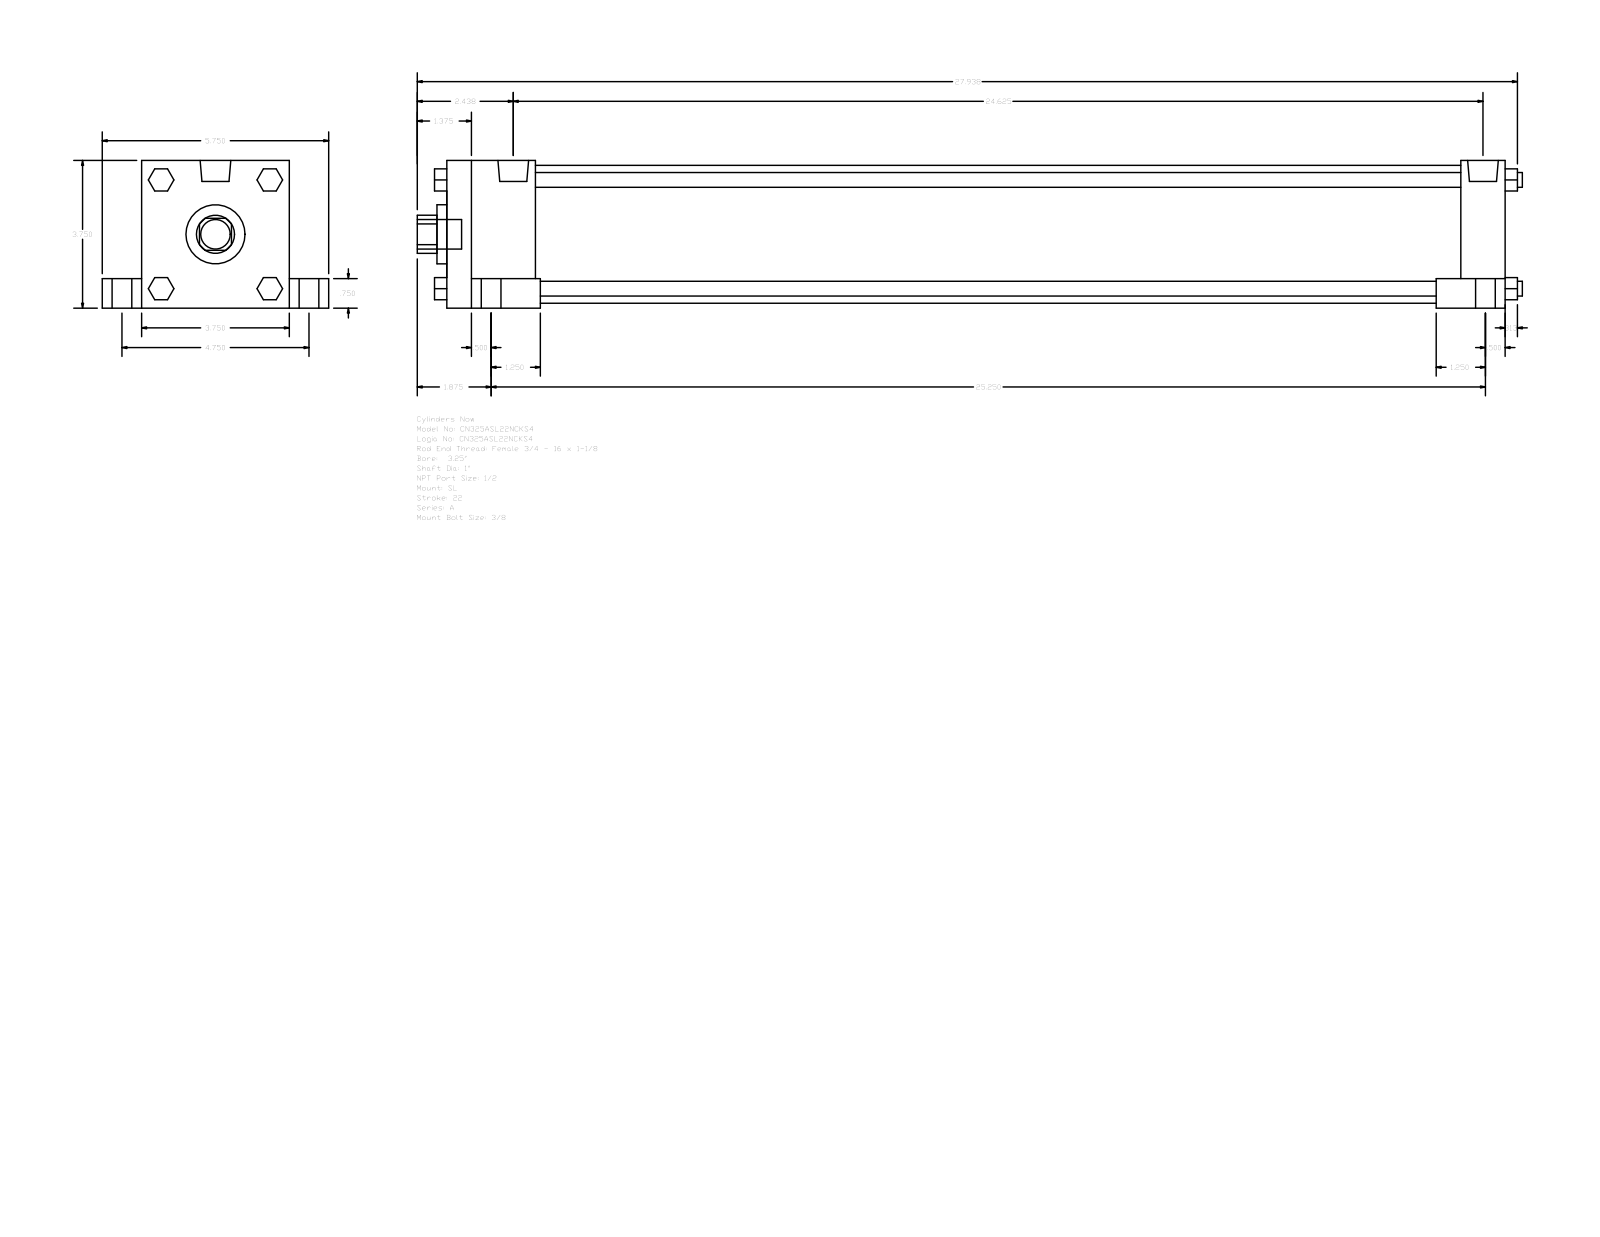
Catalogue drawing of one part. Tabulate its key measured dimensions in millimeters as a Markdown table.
| quantity | value |
| --- | --- |
| part name | A_SL__0325_1 |
| STEP written by | GSSL Pune (CONFIG_CONTROL_DESIGN) |
| units | millimeters |
| bodies | 0 solids, 150 faces (114 planar, 36 cylindrical, 0 other) |
| overall size | 712.79 × 146.05 × 95.25 |
| round holes (diameter × count) | 25.4 × 1, 38.1 × 1, 88.9 × 1 |
| round bosses / shafts (diameter × count) | 19.05 × 5, 12.7 × 4, 9.53 × 4, 8.73 × 4, 19.77 × 2 |
| partial cylindrical surfaces (radius × count) | 12.29 × 1 |
| main face-to-face distances | 95.24, 682.62, 19.05, 25.41, 120.65, 76.19, 15.87, 28.57, 57.15, 654.05 |
